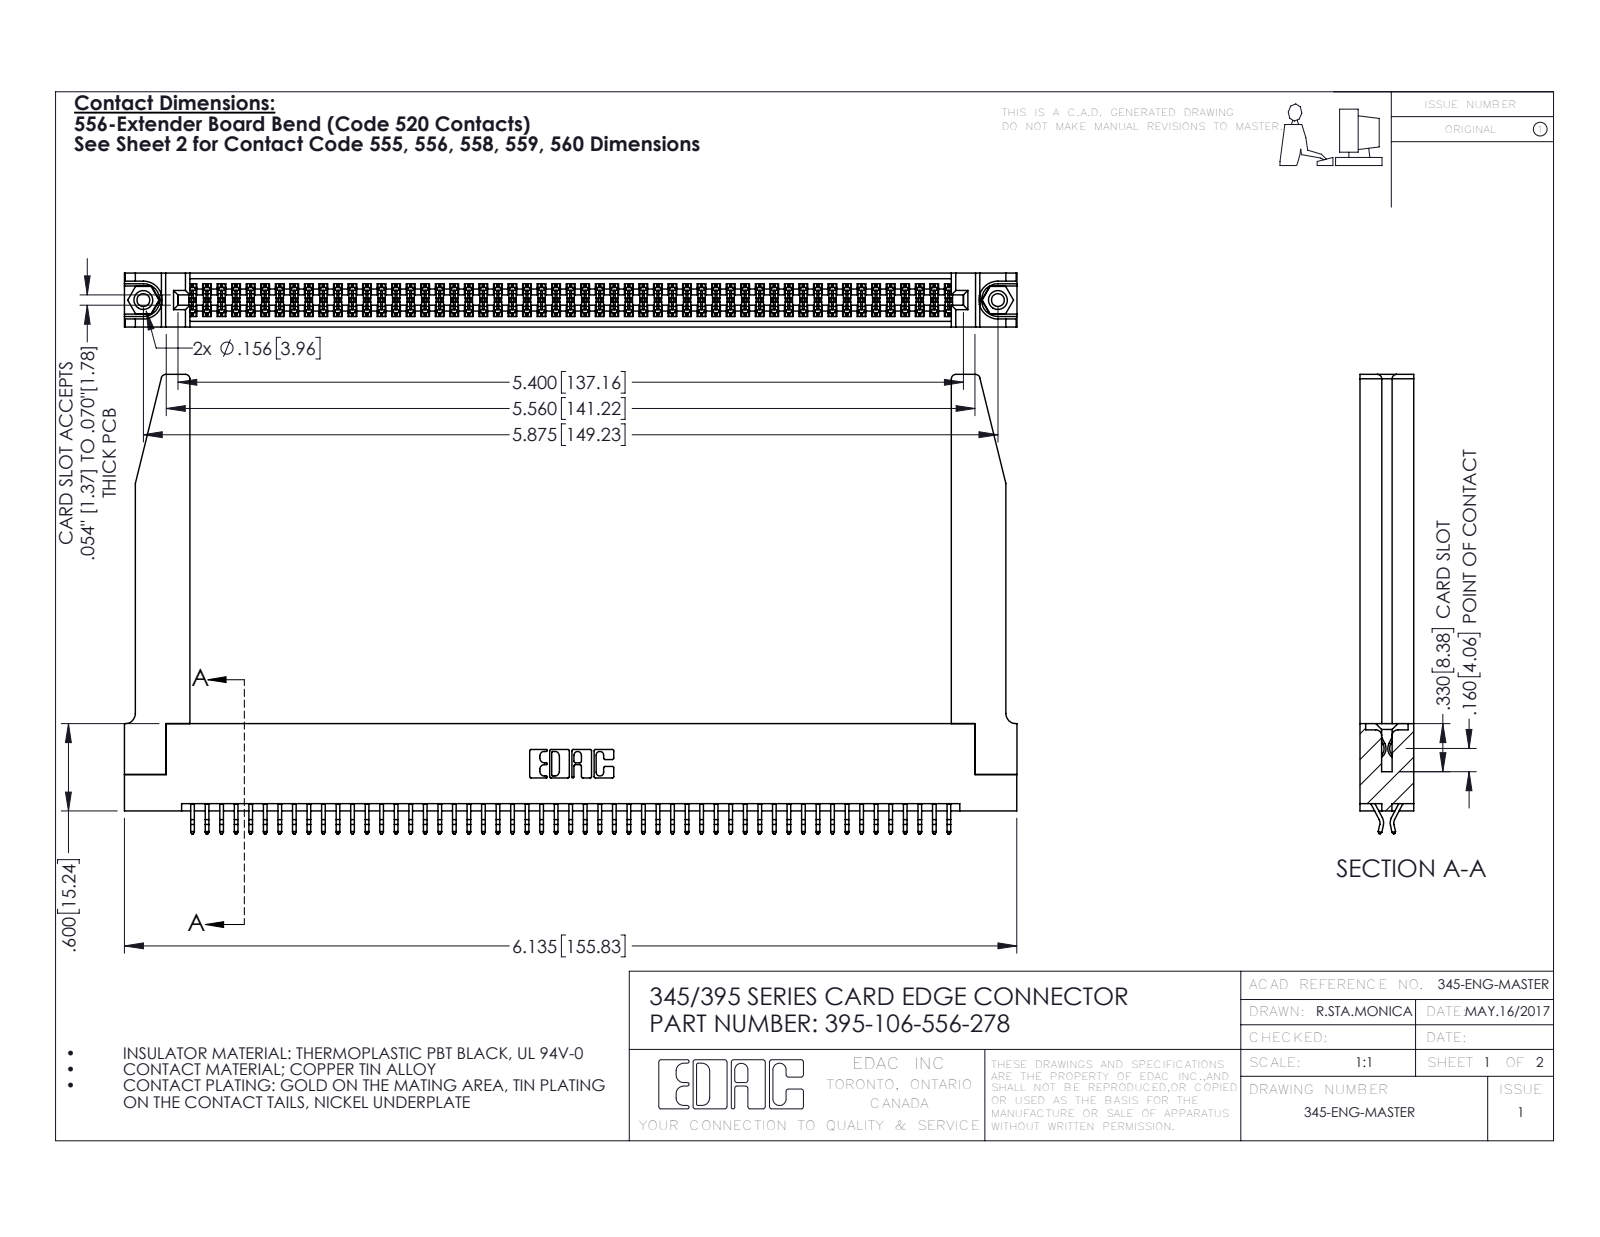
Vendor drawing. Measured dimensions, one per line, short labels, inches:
name: 395-106-556-278; 345 Part_Flush Mounting Lugs - 0.156 Dia-TH; 345-292-001_556 Tail; 345-220-078_345-220-078 (+1 more)
written by: SolidWorks 2016 (CONFIG_CONTROL_DESIGN)
unit: in
bodies: 111 solids, 6296 faces (4144 planar, 2100 cylindrical, 52 other)
size: 6.136 × 3.157 × 0.37
volume: 1.404 in³; area: 45.7 in²
holes: 2× ⌀0.089, 2× ⌀0.125, 2× ⌀0.156, 1× ⌀0.064
bosses: 2× ⌀0.155
rounds: 159× R0.006, 22× R0.01, 8× R0.03, 6× R0.007, 6× R0.031, 3× R0.026, 2× R0.01, 2× R0.014
face distances: 0.072, 0.37, 0.298, 0.2, 0.025, 0.098, 0.272, 0.225, 0.175, 0.148
hole spacings: 0.27, 5.639, 5.875
